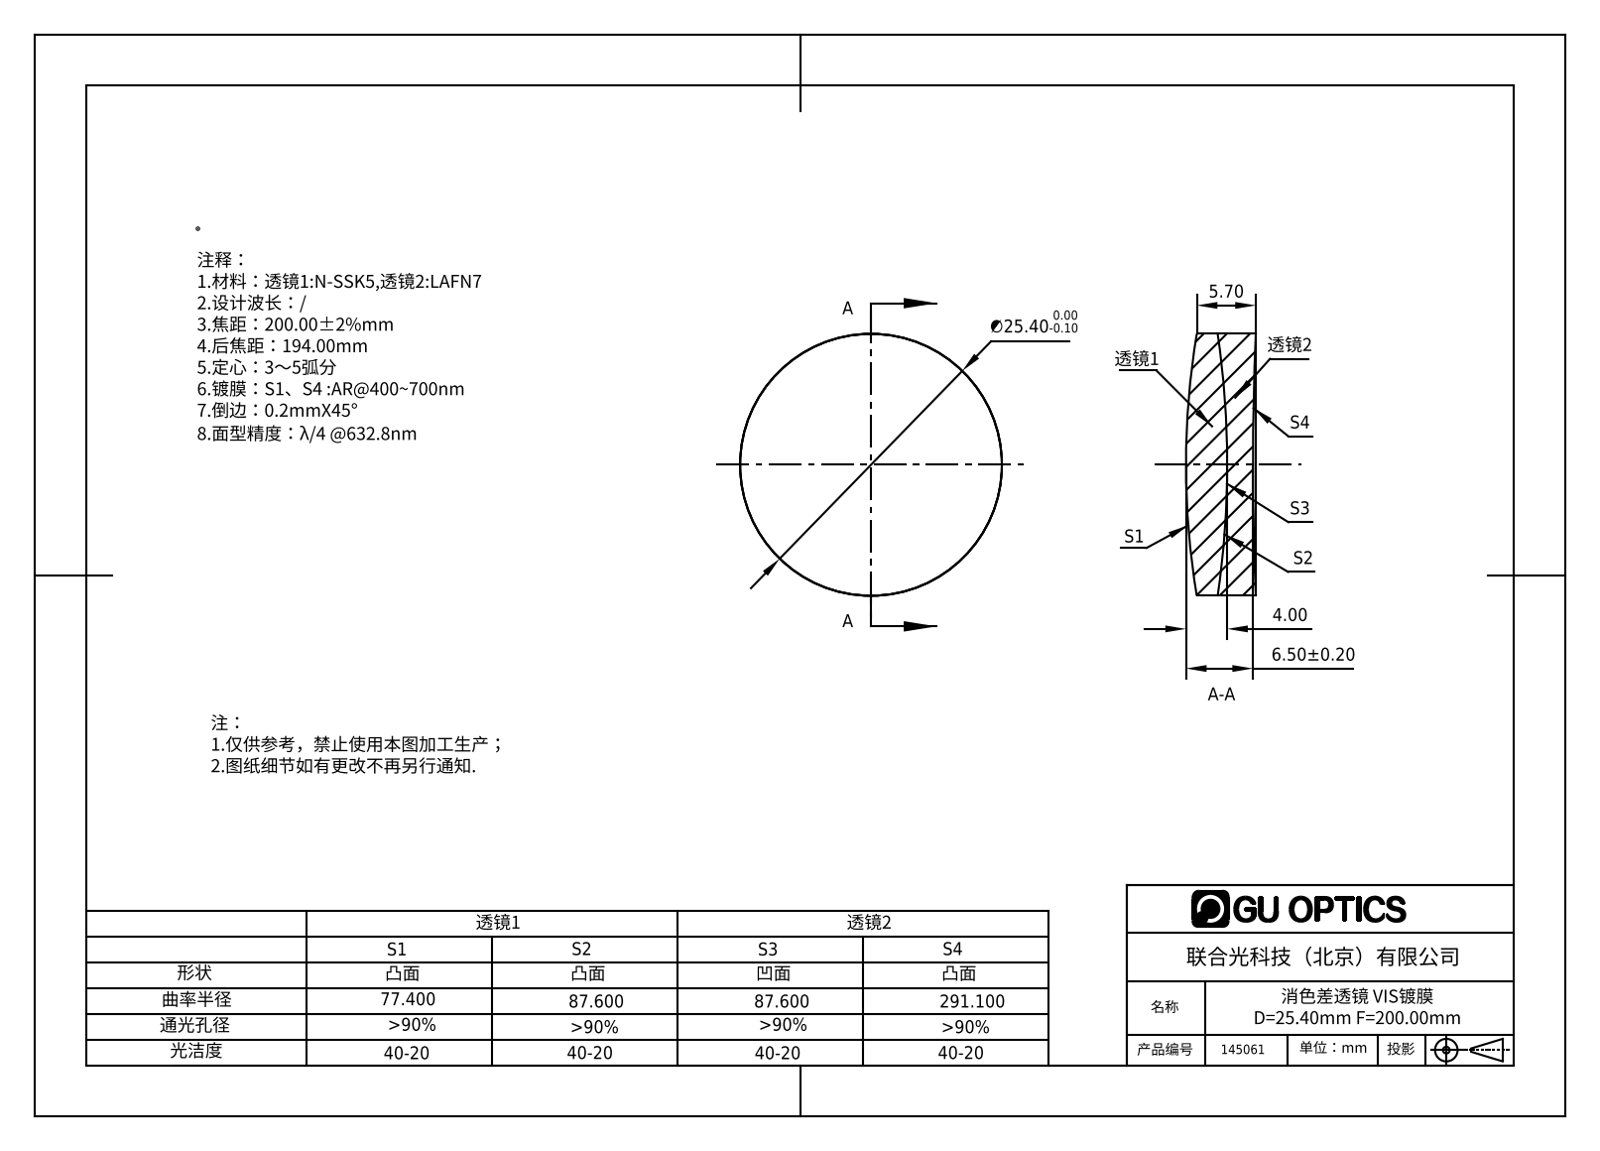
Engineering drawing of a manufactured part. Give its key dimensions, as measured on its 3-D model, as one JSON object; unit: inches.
{"part_name": "145061", "step_written_by": "SolidWorks 2016 (AUTOMOTIVE_DESIGN)", "units": "inches", "bodies": {"solids": 2, "faces": 12, "planar": 0, "cylindrical": 4, "other": 8}, "overall_size": [1, 1, 0.267], "volume_in3": 0.189, "surface_area_in2": 3.864, "round_bosses_or_shafts": [[1, 1]]}
